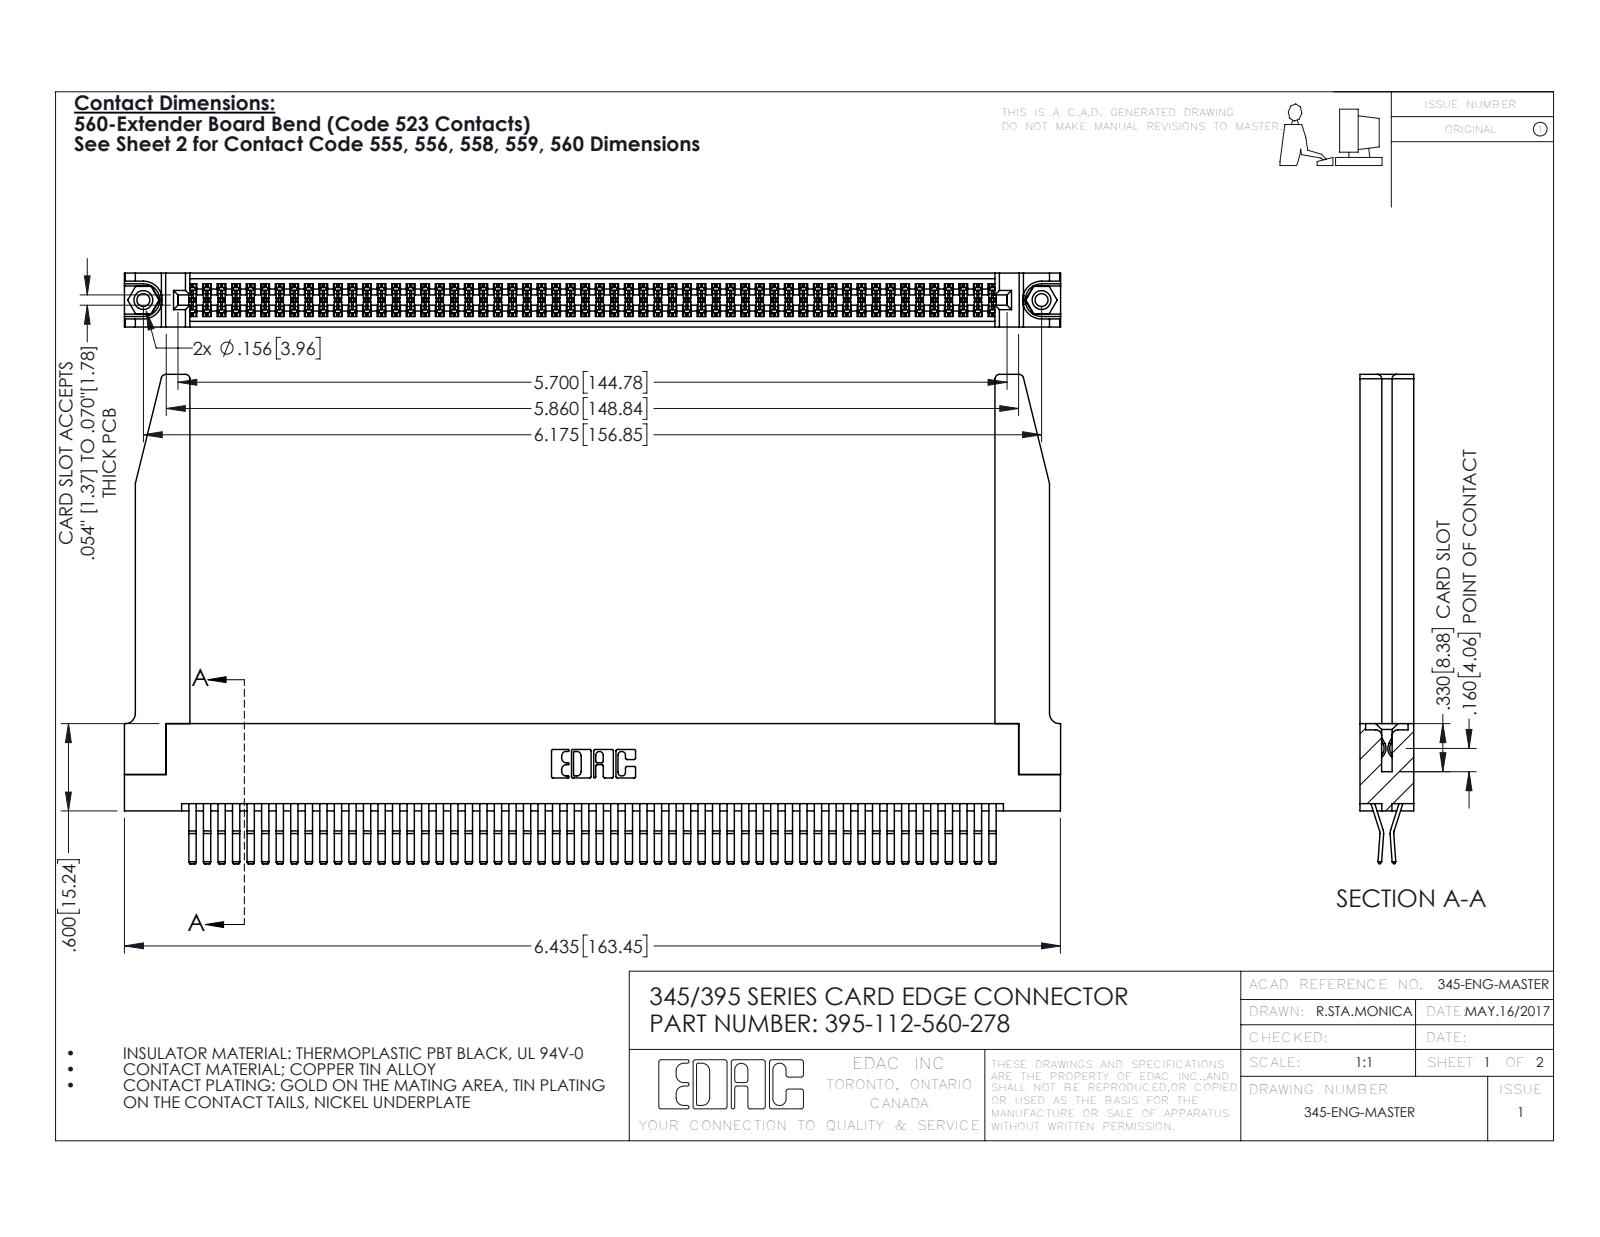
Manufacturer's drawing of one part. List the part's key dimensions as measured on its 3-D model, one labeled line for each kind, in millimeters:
Part name (STEP PRODUCT): 345 Part_Flush Mounting Lugs - 0.156 Dia-TH; 345-292-001_560 Tail; 345-250-001_345-250-001-102; 345-220-078_345-220-078 (+1 more)
STEP written by: SolidWorks 2016 (CONFIG_CONTROL_DESIGN)
Units: millimetres
Bodies: 117 solids, 6184 faces (3918 planar, 2214 cylindrical, 52 other)
Overall size (bounding box): 163.5 × 85.4 × 9.4
Volume: 24 520 mm³ · Surface area: 33 750 mm²
Round holes (diameter × count): ⌀2.3 ×2, ⌀3.2 ×2, ⌀4 ×2, ⌀1.6 ×1
Round bosses / shafts (diameter × count): ⌀3.9 ×2
Partial cylindrical surfaces — rounded edges, fillets, slot ends (radius × count): R0.2 ×168, R0.3 ×22, R0.8 ×8, R0.2 ×6, R0.8 ×6, R0.7 ×3, R0.3 ×2, R0.4 ×2
Main face-to-face distances: 1.8, 9.4, 7.6, 0.6, 5.1, 2.5, 6.9, 5.7, 4.4, 3.8
Hole centre spacings: 6.9, 150.9, 156.8
